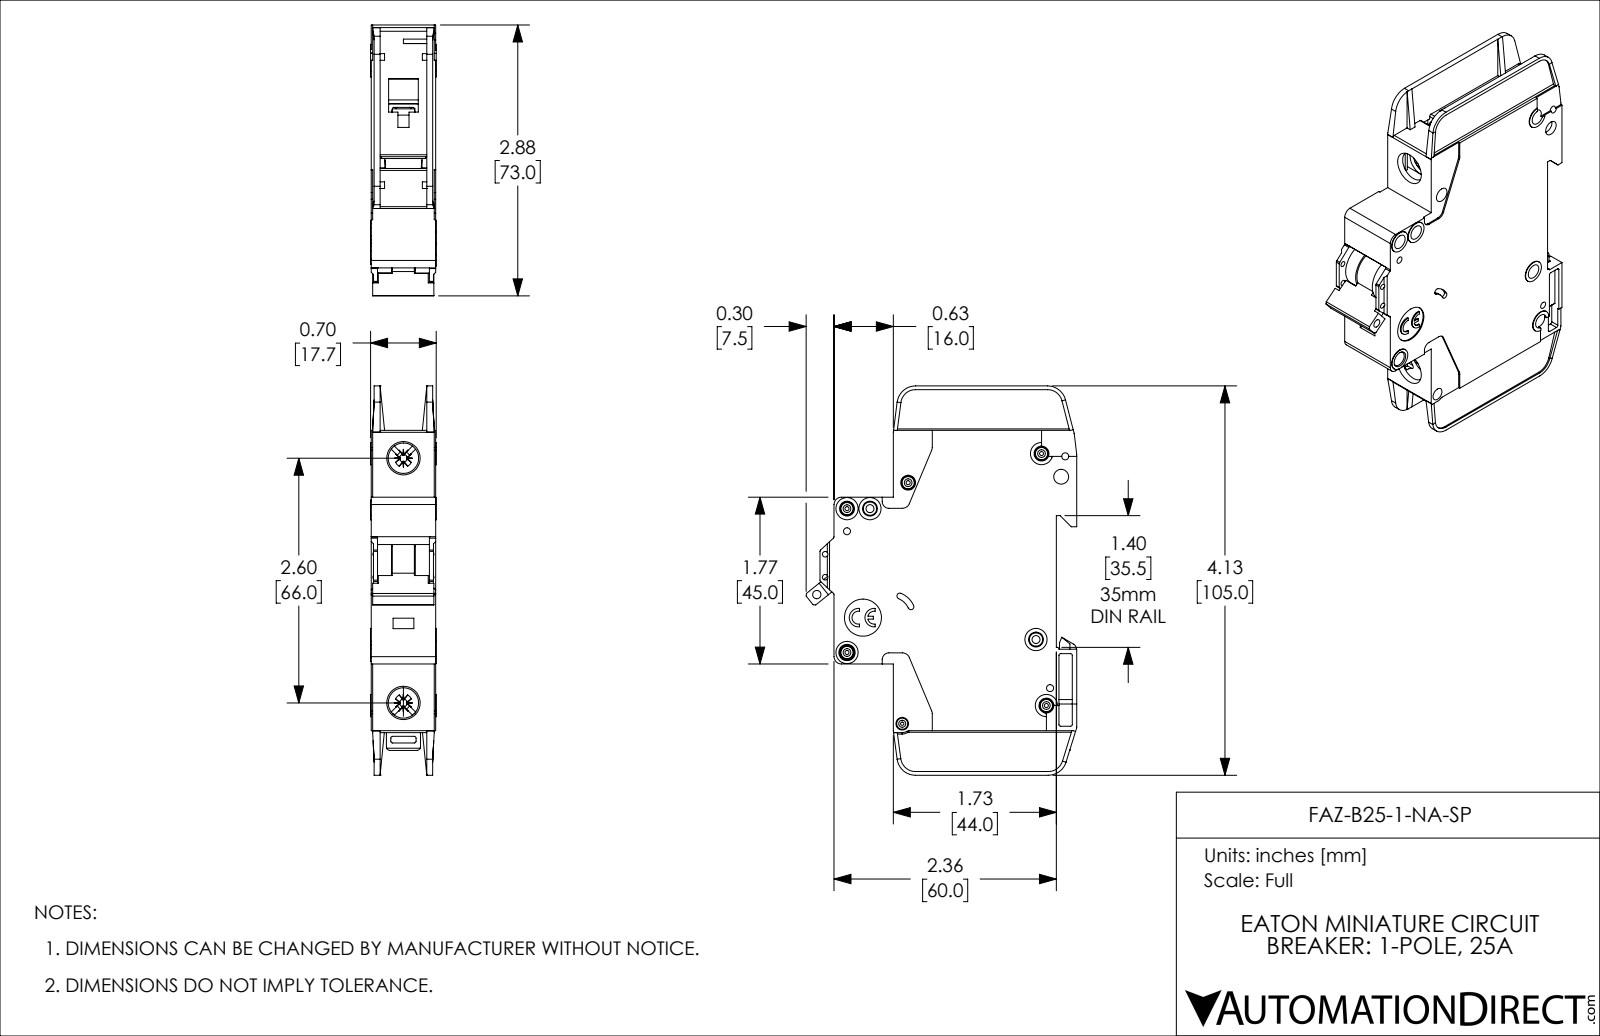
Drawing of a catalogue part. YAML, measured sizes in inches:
part_name: "FAZ-B25-1-NA-SP"
step_written_by: "SolidWorks 2019 (AUTOMOTIVE_DESIGN)"
units: inches
bodies: {solids: 1, faces: 1127, planar: 671, cylindrical: 357, other: 99}
overall_size: [4.134, 2.876, 0.697]
volume: 4.682
surface_area: 41.01
round_holes:
  - {diameter: 0.157, count: 8}
  - {diameter: 0.043, count: 5}
  - {diameter: 0.075, count: 4}
  - {diameter: 0.059, count: 2}
  - {diameter: 0.085, count: 2}
  - {diameter: 0.323, count: 2}
  - {diameter: 0.035, count: 1}
  - {diameter: 0.089, count: 1}
  - {diameter: 0.098, count: 1}
  - {diameter: 0.134, count: 1}
  - {diameter: 0.394, count: 1}
round_bosses_or_shafts:
  - {diameter: 0.13, count: 5}
  - {diameter: 0.236, count: 4}
  - {diameter: 0.118, count: 2}
  - {diameter: 0.098, count: 1}
partial_cylinders:
  - {radius: 0.02, count: 42}
  - {radius: 0.016, count: 10}
  - {radius: 0.039, count: 10}
  - {radius: 0.079, count: 8}
  - {radius: 0.197, count: 5}
  - {radius: 0.008, count: 4}
  - {radius: 0.026, count: 4}
  - {radius: 0.043, count: 4}
face_to_face_distances: [0.047, 0.685, 0.591, 0.638, 0.094, 0.543, 0.016, 0.031, 0.496, 0.575]
hole_center_spacings: [0.244, 0.537, 0.87, 0.189, 0.199, 0.204, 0.221, 0.24]
